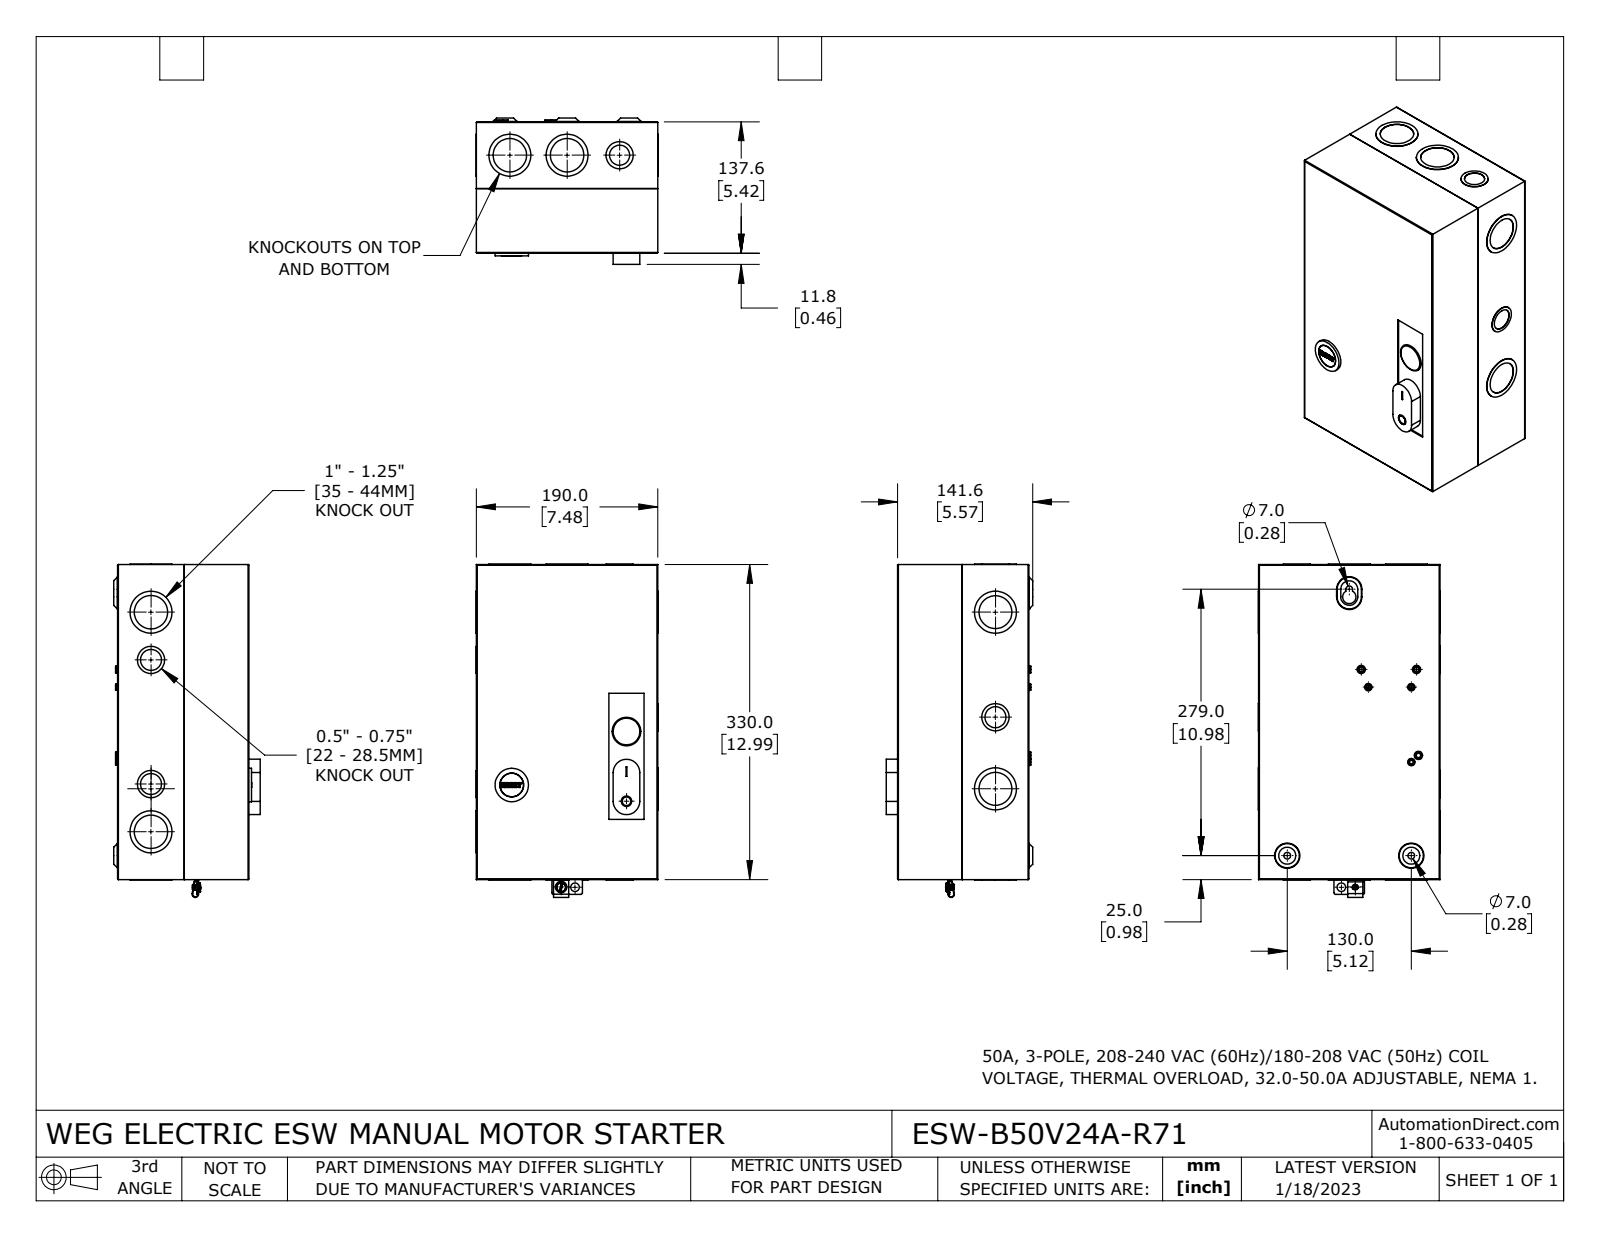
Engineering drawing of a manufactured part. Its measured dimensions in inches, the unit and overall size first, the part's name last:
Units: inches
Overall size (bounding box): 13.74 × 7.504 × 6.039
Round holes (diameter × count): ⌀1.378 ×4, ⌀0.146 ×3, ⌀0.183 ×3, ⌀0.276 ×2, ⌀0.866 ×2, ⌀0.886 ×2, ⌀1.357 ×2, ⌀0.256 ×1, ⌀0.279 ×1, ⌀0.354 ×1, ⌀0.433 ×1, ⌀0.469 ×1
Round bosses / shafts (diameter × count): ⌀1.732 ×4, ⌀1.122 ×3, ⌀0.278 ×3, ⌀0.24 ×3, ⌀1.734 ×2, ⌀1.378 ×1, ⌀1.193 ×1, ⌀1.148 ×1
Partial cylindrical surfaces — rounded edges, fillets, slot ends (radius × count): R0.004 ×34, R0.031 ×8, R0.079 ×3, R0.138 ×3, R0.059 ×2, R0.075 ×2, R0.108 ×2, R0.122 ×2
Main face-to-face distances: 0.047, 5.37, 7.433, 5.323, 5.417, 12.945, 7.386, 7.48, 0.071, 12.898
Hole centre spacings: 0.571, 1.772, 1.969, 2.283, 2.362, 5.118, 7.087, 10.972
Volume: 24.58 in³ · Surface area: 936.7 in²
Bodies: 7 solids, 435 faces (161 planar, 221 cylindrical, 53 other)
Part name (STEP PRODUCT): ESW-B50V24A-R71
STEP written by: SolidWorks 2021 (CONFIG_CONTROL_DESIGN)
